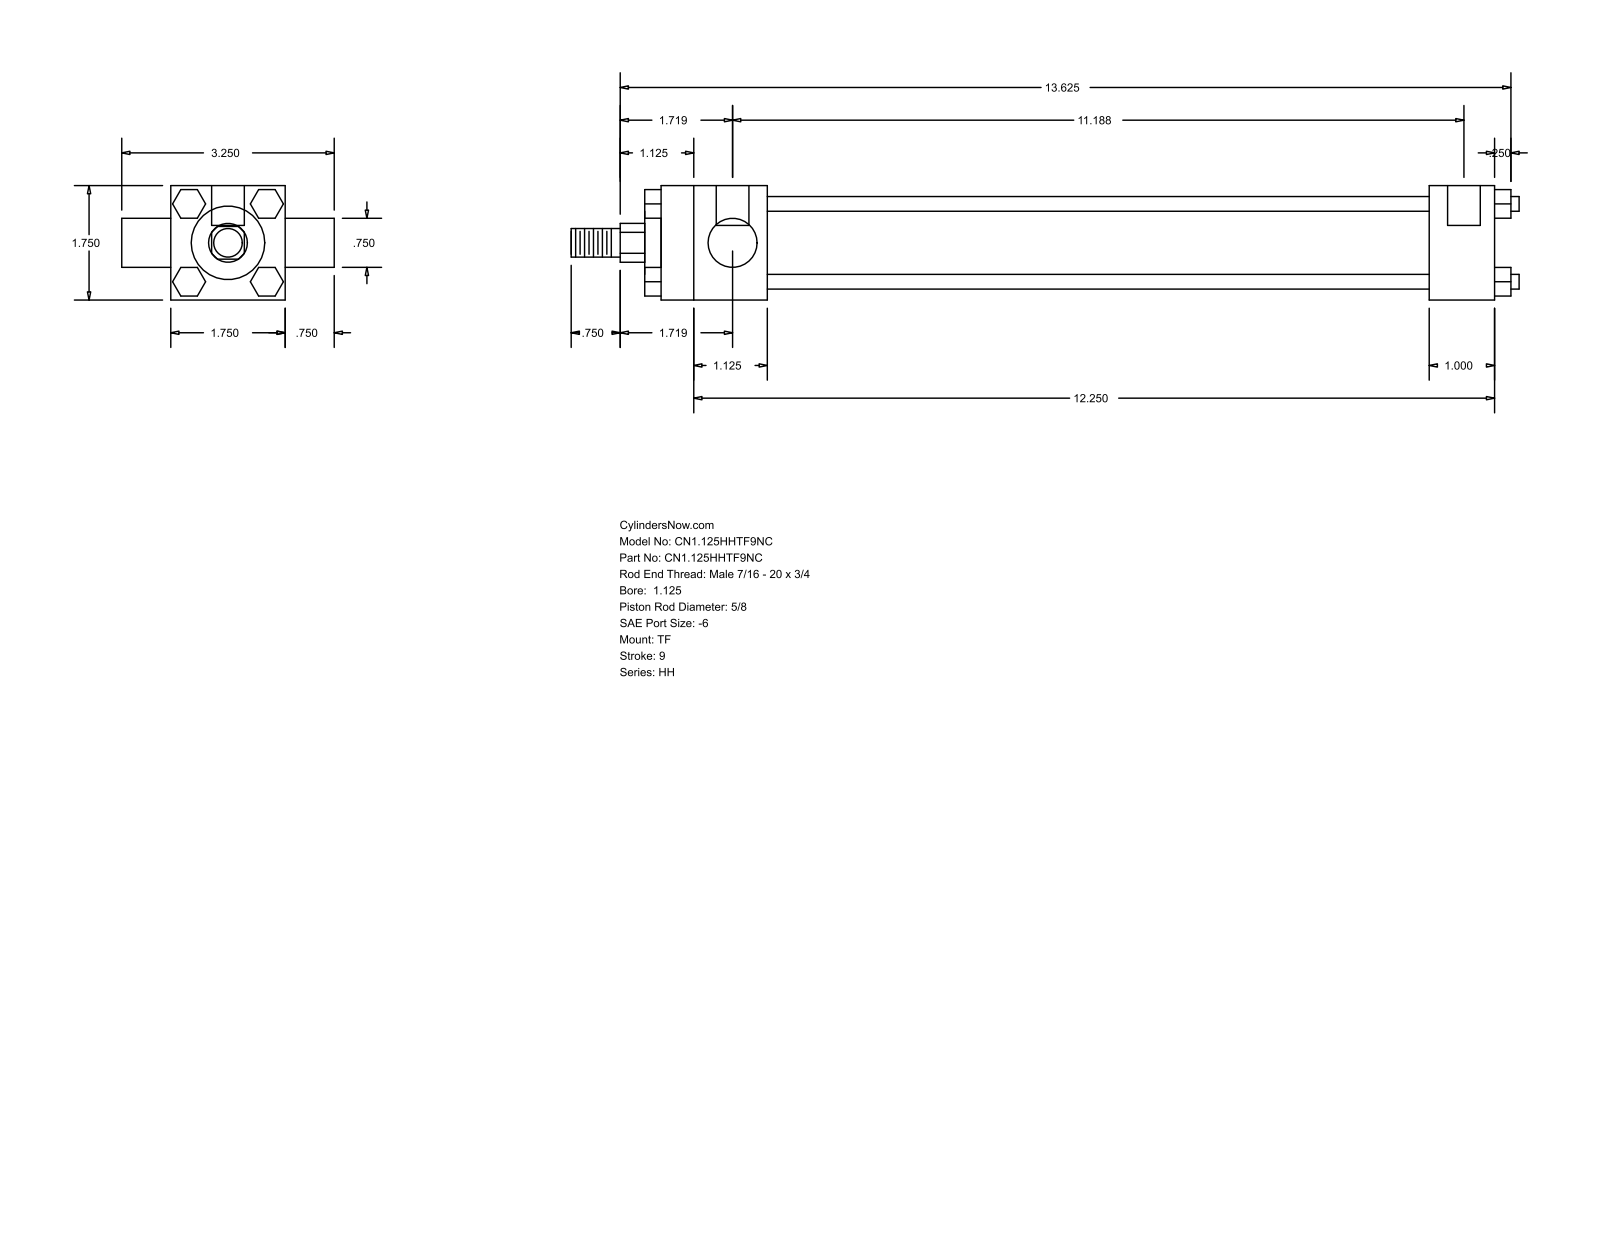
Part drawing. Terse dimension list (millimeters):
name: HH_TF__0112_0.625
written by: GSSL Pune (CONFIG_CONTROL_DESIGN)
unit: mm
bodies: 0 solids, 120 faces (92 planar, 28 cylindrical, 0 other)
size: 368.3 × 82.55 × 44.45
holes: 3× ⌀5.56, 2× ⌀12.7
bosses: 4× ⌀5.71, 1× ⌀34.92, 1× ⌀28.57, 1× ⌀19.05, 1× ⌀15.88, 1× ⌀11.11
rounds: 1× R7.54
face distances: 44.46, 11.11, 257.17, 282.58, 25.41, 41.27, 298.44, 323.85, 47.62, 6.35
hole spacings: 3.17, 280.99, 284.16
